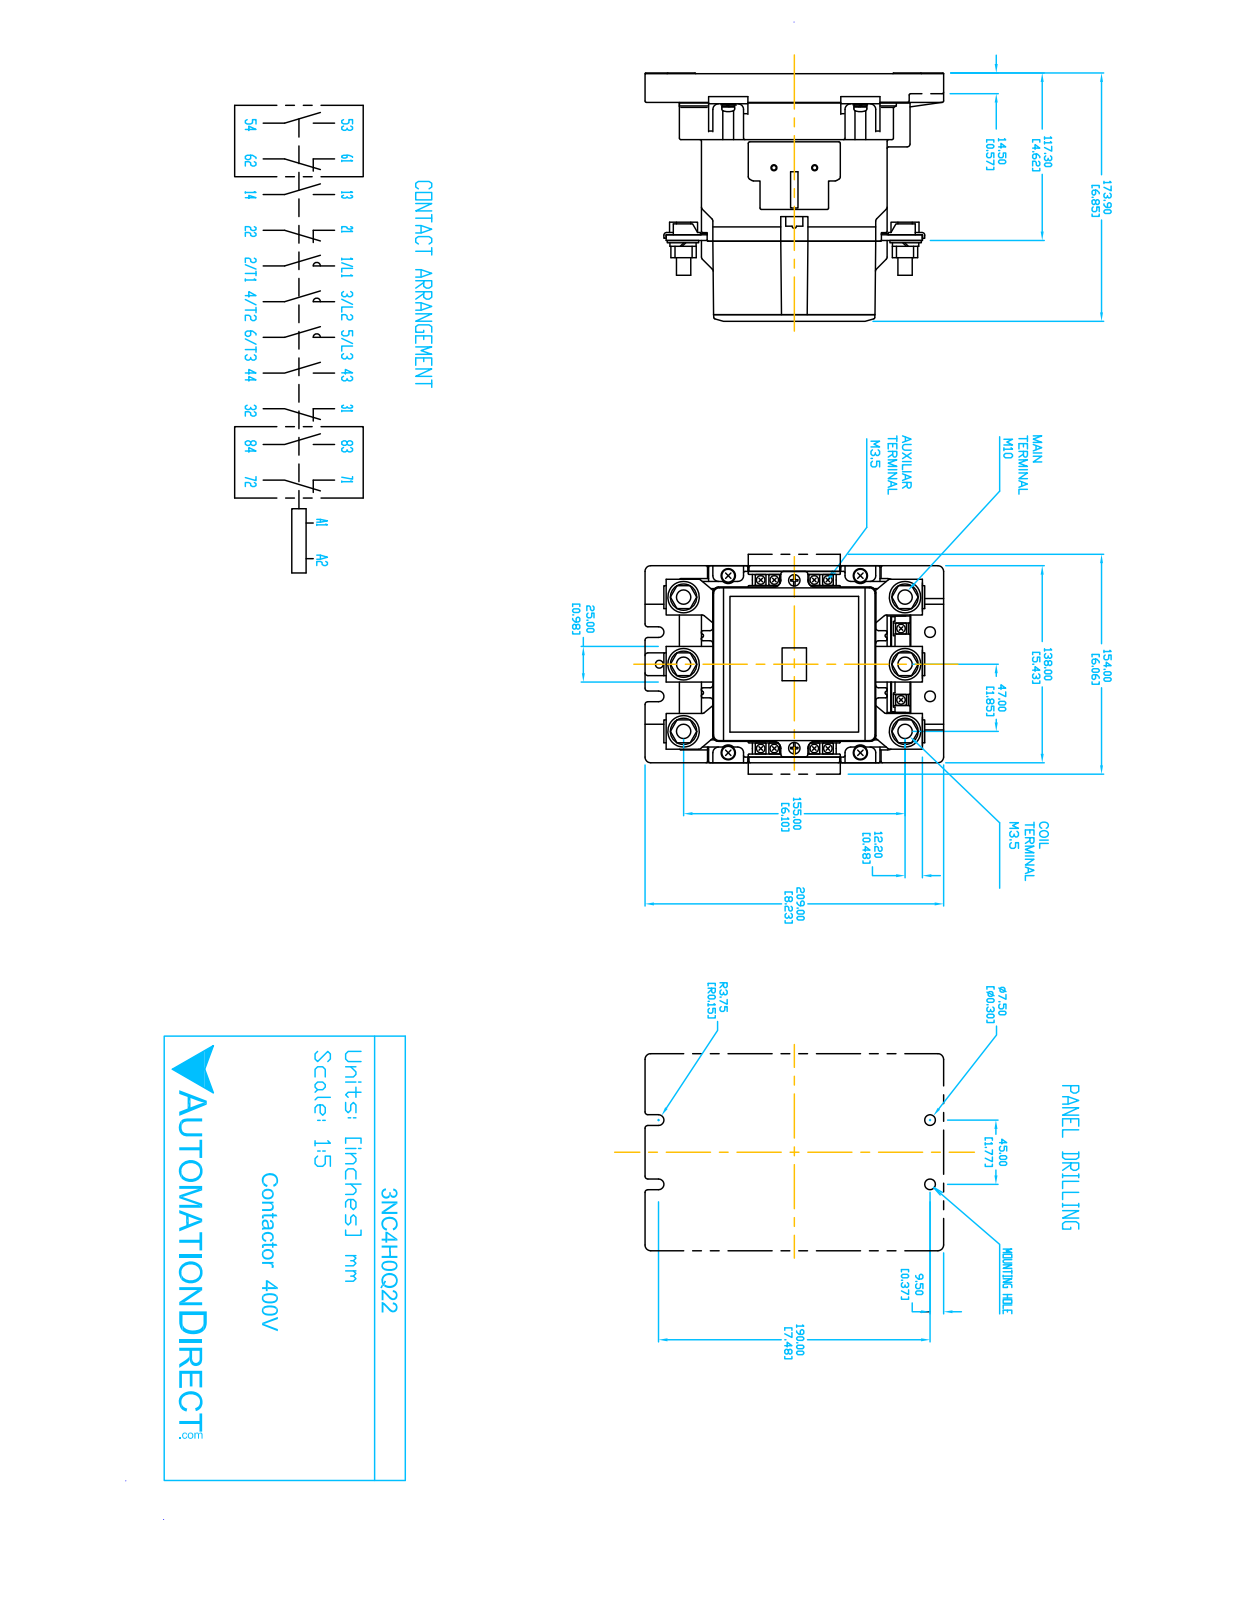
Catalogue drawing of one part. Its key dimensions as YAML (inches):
part_name: "3NC4H0Q22"
step_written_by: "SolidWorks 2018 (AUTOMOTIVE_DESIGN)"
units: inches
bodies: {solids: 20, faces: 376, planar: 258, cylindrical: 118, other: 0}
overall_size: [8.228, 6.929, 5.433]
volume: 179.6
surface_area: 327
round_holes:
  - {diameter: 0.315, count: 8}
  - {diameter: 0.394, count: 6}
  - {diameter: 0.295, count: 2}
partial_cylinders:
  - {radius: 0.079, count: 22}
  - {radius: 0.157, count: 16}
  - {radius: 0.031, count: 8}
  - {radius: 0.039, count: 8}
  - {radius: 0.197, count: 4}
  - {radius: 0.217, count: 4}
  - {radius: 0.02, count: 2}
  - {radius: 0.148, count: 2}
face_to_face_distances: [4.72, 4.843, 0.591, 4.736, 0.016, 4.252, 6.929, 2.209, 2.193, 0.315]
hole_center_spacings: [1.85, 3.087, 3.835, 5.17, 6.377, 6.102, 1.122, 1.185]
